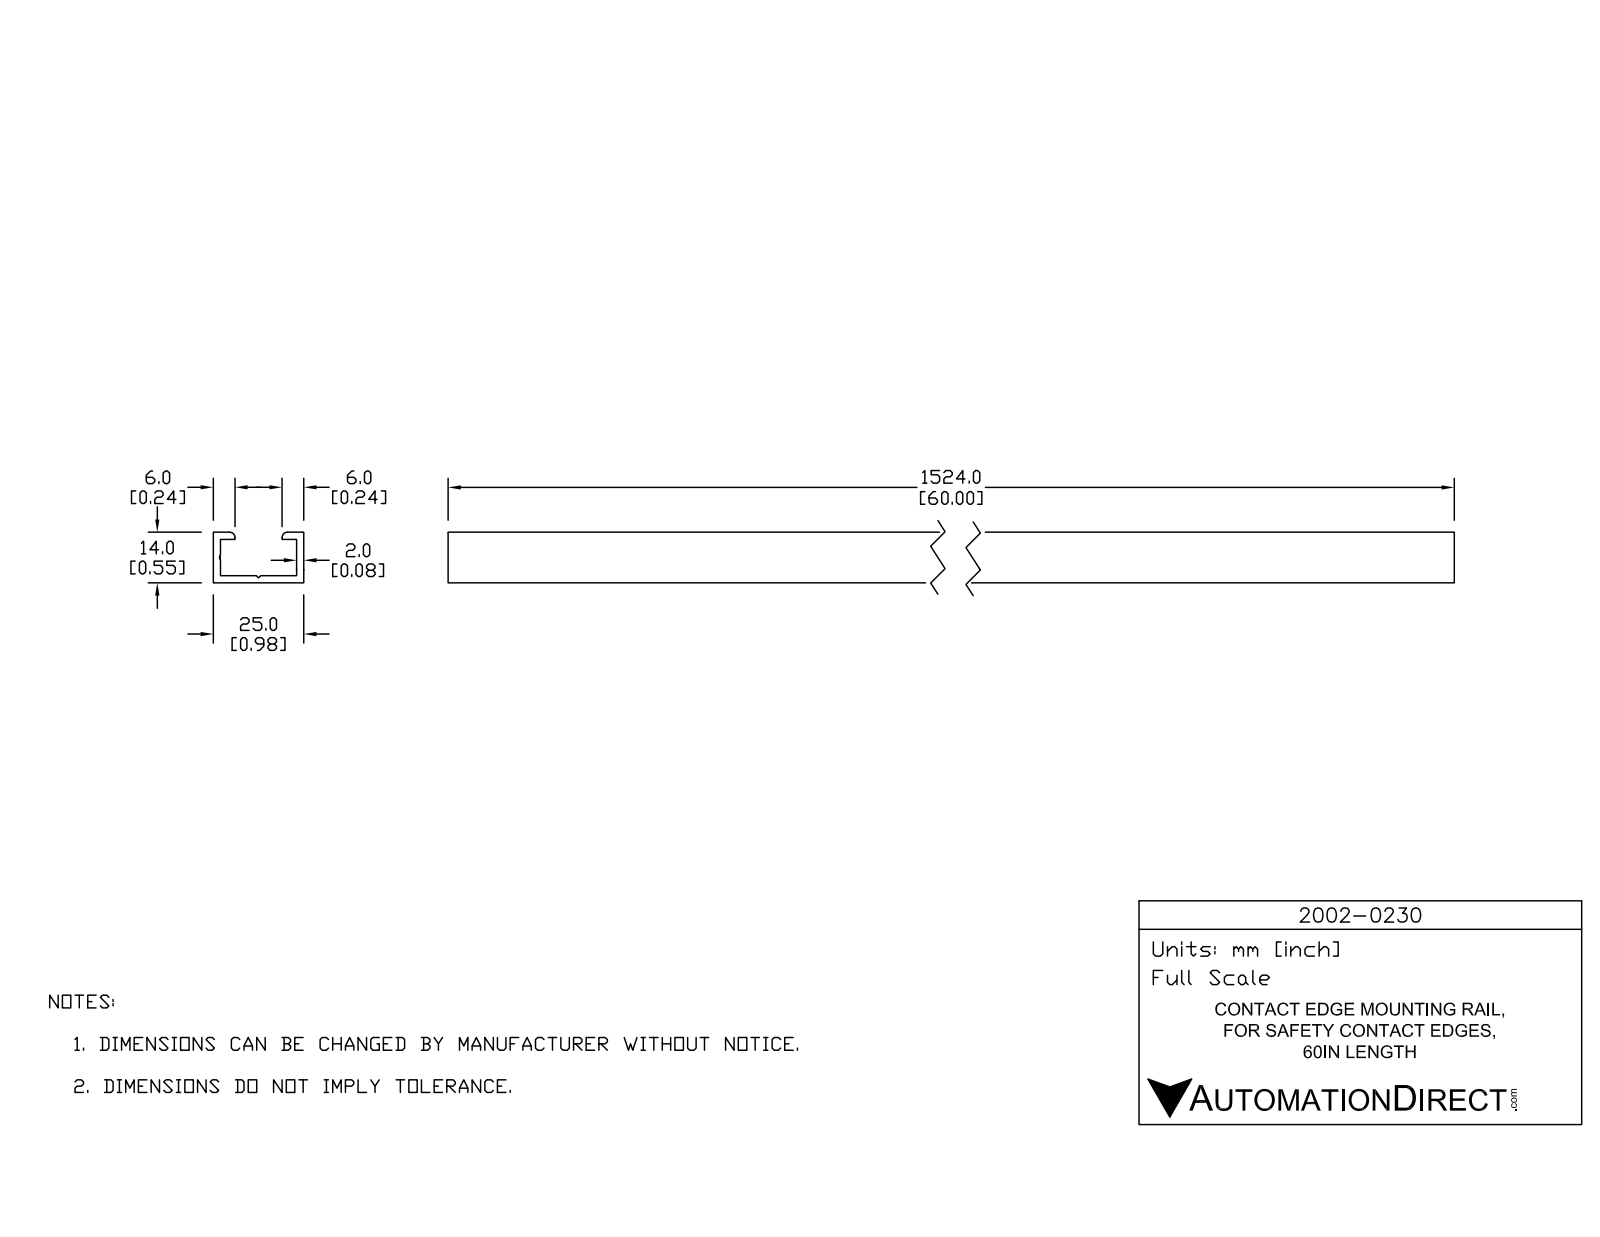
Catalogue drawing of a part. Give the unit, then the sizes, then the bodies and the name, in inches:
Units: inches
Overall size (bounding box): 60 × 0.984 × 0.551
Partial cylindrical surfaces — rounded edges, fillets, slot ends (radius × count): R0.008 ×4, R0.059 ×2
Main face-to-face distances: 0.079, 0.906, 0.472, 0.984, 0.827, 0.551, 0.394, 0.236, 0.748, 0.157
Volume: 10.46 in³ · Surface area: 277.6 in²
Bodies: 1 solid, 28 faces (22 planar, 6 cylindrical, 0 other)
Part name (STEP PRODUCT): 2002-0230
STEP written by: SolidWorks 2017 (AUTOMOTIVE_DESIGN)
